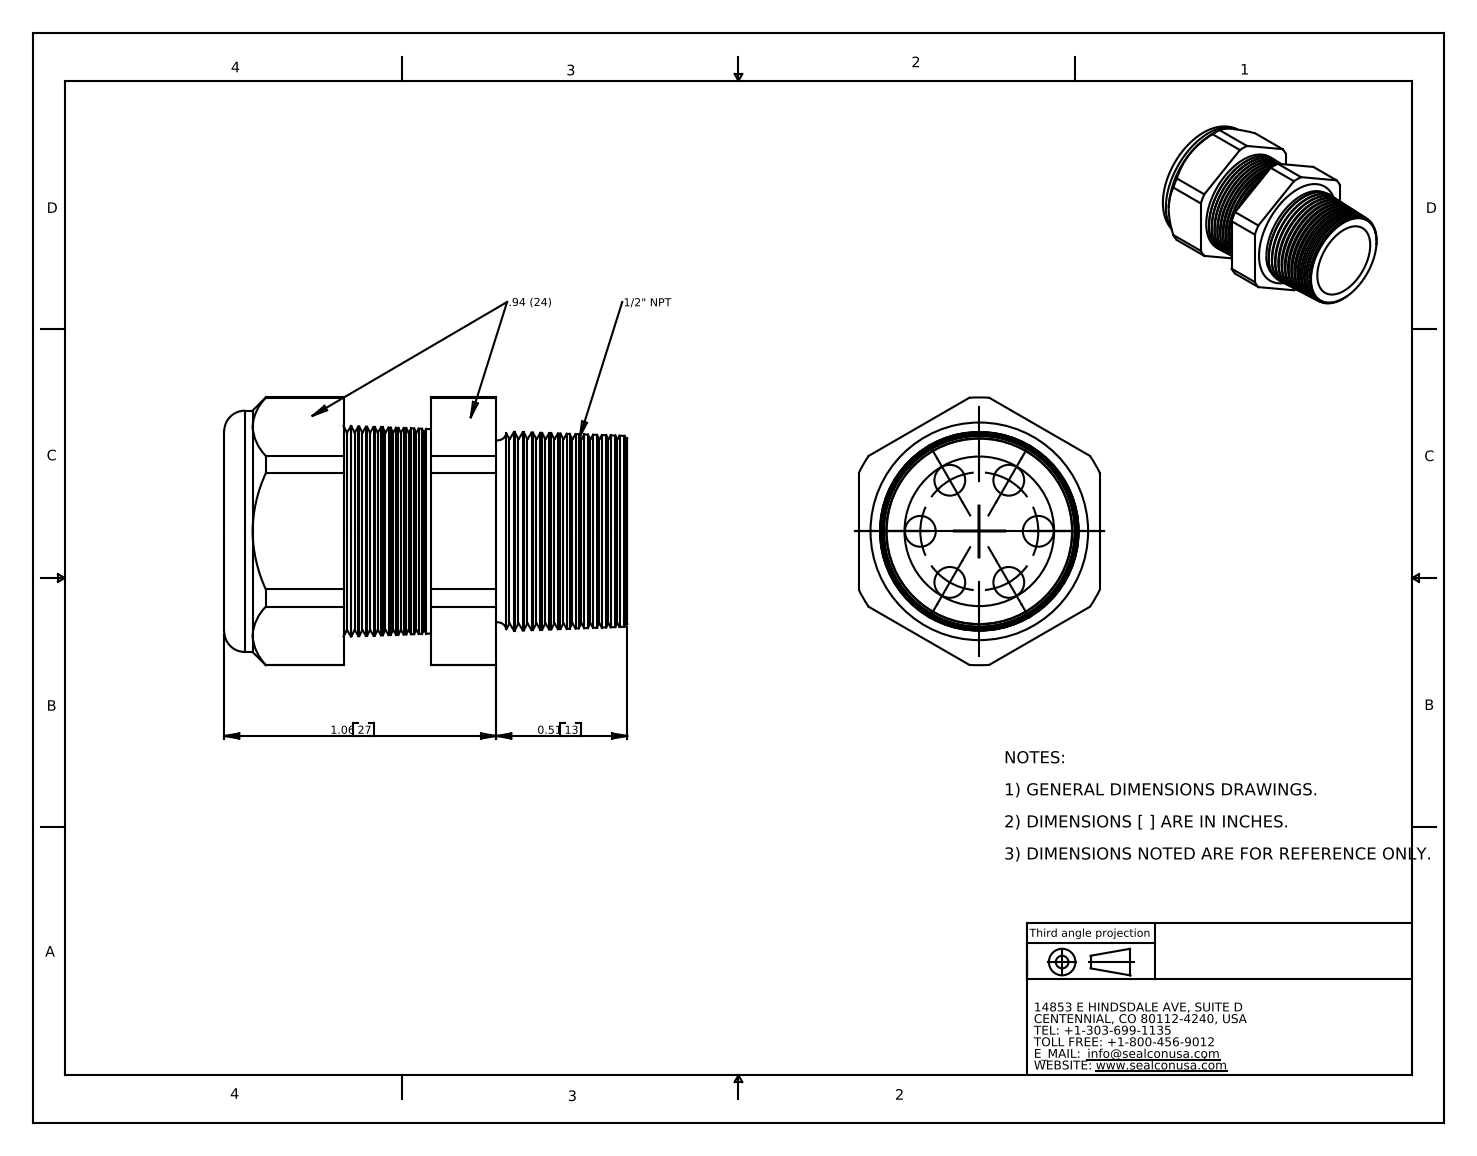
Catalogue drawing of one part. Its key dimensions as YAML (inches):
part_name: "CD13N2-GY"
step_written_by: "SolidWorks 2007 (CONFIG_CONTROL_DESIGN)"
units: inches
bodies: {solids: 2, faces: 216, planar: 20, cylindrical: 32, other: 164}
overall_size: [1.57, 1.043, 0.94]
volume: 0.556
surface_area: 11.93
round_holes:
  - {diameter: 0.12, count: 6}
  - {diameter: 0.58, count: 1}
  - {diameter: 0.6, count: 1}
round_bosses_or_shafts:
  - {diameter: 0.94, count: 1}
partial_cylinders:
  - {radius: 0.522, count: 1}
face_to_face_distances: [0.94, 0.34, 0.115, 0.454, 0.35, 0.465, 0.804, 0.02, 0.33, 0.444]
hole_center_spacings: [0.23, 0.23, 0.398, 0.398, 0.459, 0.46]
